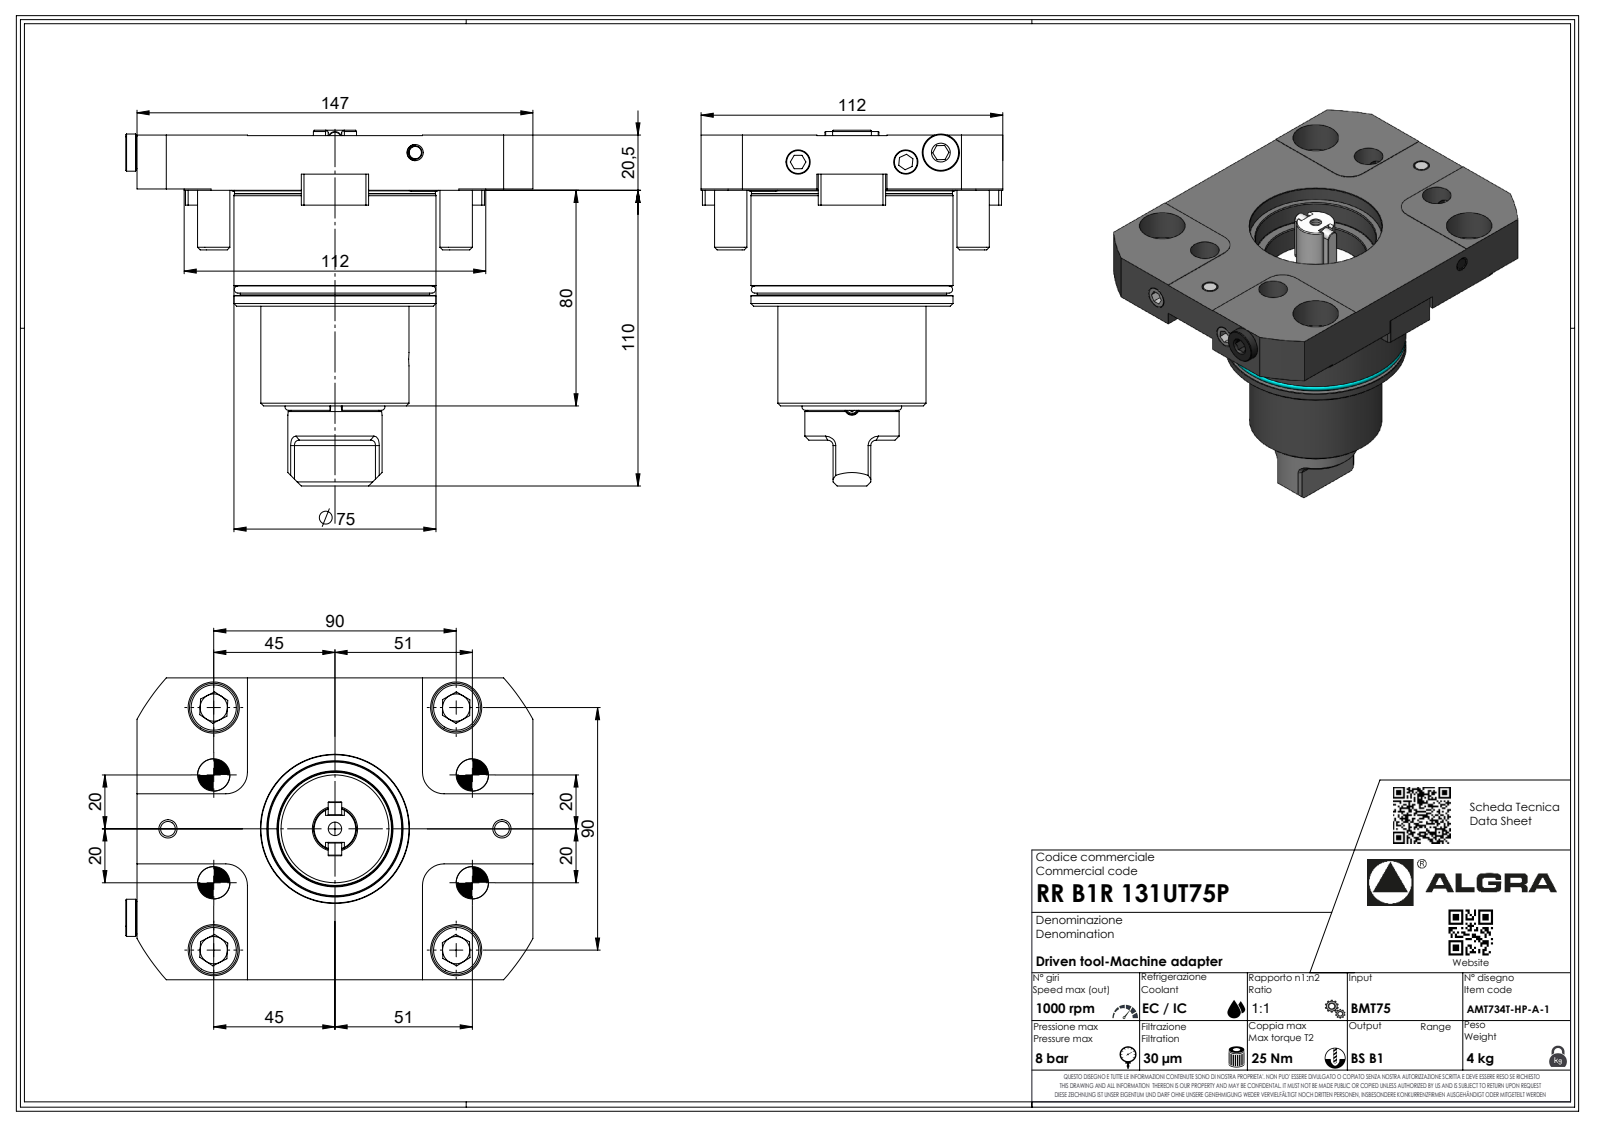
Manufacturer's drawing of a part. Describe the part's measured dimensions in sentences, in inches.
The part is named "RRB1R131UT75P". Its 3-D file was written by "SolidWorks 2023 (AUTOMOTIVE_DESIGN)". It is 1 solid with 452 faces: 310 planar, 56 cylindrical and 86 other. Overall it measures 5.787 by 5.197 by 4.409 inches. Its volume is 38.26 cubic inches and its surface area 103.3 square inches. Round holes: 1 of diameter 0.083, 1 of diameter 0.197. Round bosses or shafts: 1 of diameter 2.953, 1 of diameter 2.937, 1 of diameter 2.768, 1 of diameter 2.165, 1 of diameter 1.378, 1 of diameter 0.63, 1 of diameter 0.251, 1 of diameter 0.067. Partial cylindrical surfaces (rounded edges, fillets, slot ends): 12 of radius 0.157, 7 of radius 0.013, 7 of radius 0.02, 7 of radius 0.146, 4 of radius 0.394, 2 of radius 0.079, 1 of radius 0.008, 1 of radius 3.307. The main face-to-face distances are 0.807, 0.02, 0.787, 0.217, 0.236, 1.693, 4.409, 1.713, 1.929, 2.5.
